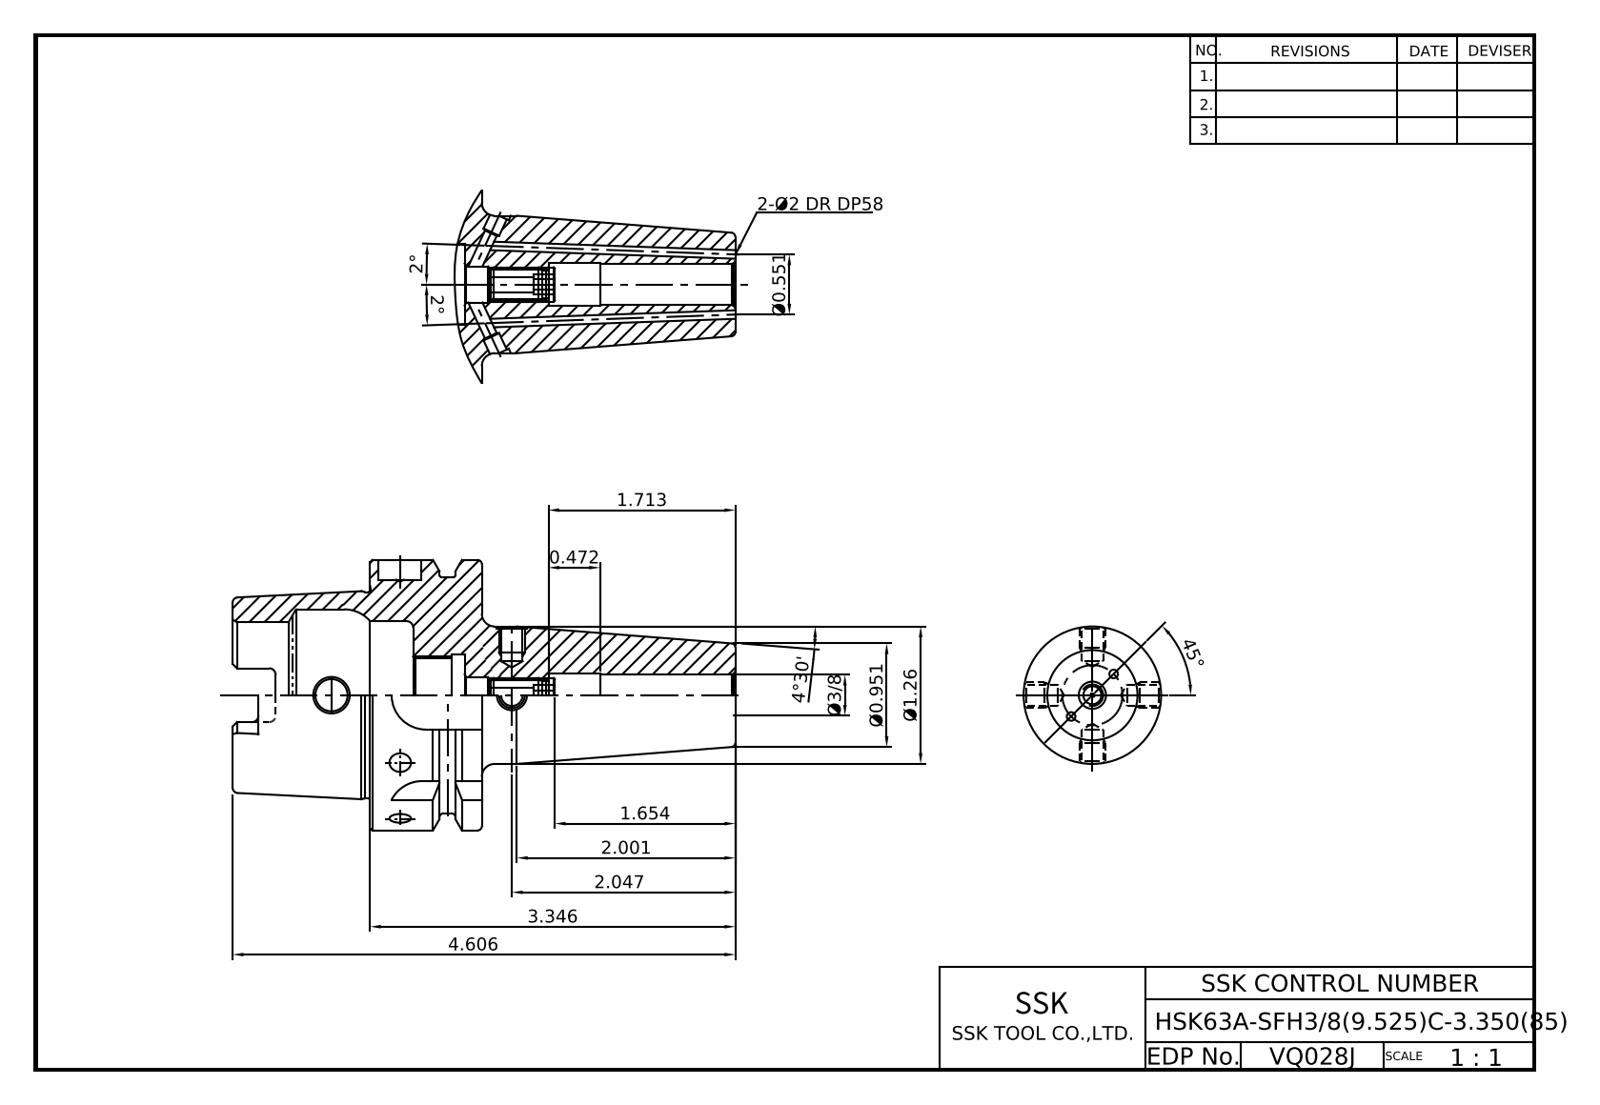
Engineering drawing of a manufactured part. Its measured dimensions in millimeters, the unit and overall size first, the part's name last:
Units: millimetres
Overall size (bounding box): 117 × 63 × 63
Round holes (diameter × count): ⌀2 ×2, ⌀5 ×2, ⌀6 ×2, ⌀7 ×1, ⌀7.5 ×1, ⌀8 ×1, ⌀8.4 ×1, ⌀9.53 ×1, ⌀10 ×1, ⌀10.12 ×1, ⌀17 ×1, ⌀18 ×1
Round bosses / shafts (diameter × count): ⌀63 ×1, ⌀55 ×1, ⌀48.04 ×1, ⌀32 ×1
Partial cylindrical surfaces — rounded edges, fillets, slot ends (radius × count): R1.5 ×6, R2.88 ×4, R8 ×4
Main face-to-face distances: 26, 10, 16, 32, 6.12, 9.88, 42, 58, 4, 22
Hole centre spacings: 31, 47
Volume: 114 824 mm³ · Surface area: 31 224 mm²
Bodies: 1 solid, 208 faces (65 planar, 73 cylindrical, 70 other)
Part name (STEP PRODUCT): VQ028J-HSK63A-SFH0_375C-3_35
STEP written by: CREO PARAMETRIC BY PTC INC, 2018100 (CONFIG_CONTROL_DESIGN)
